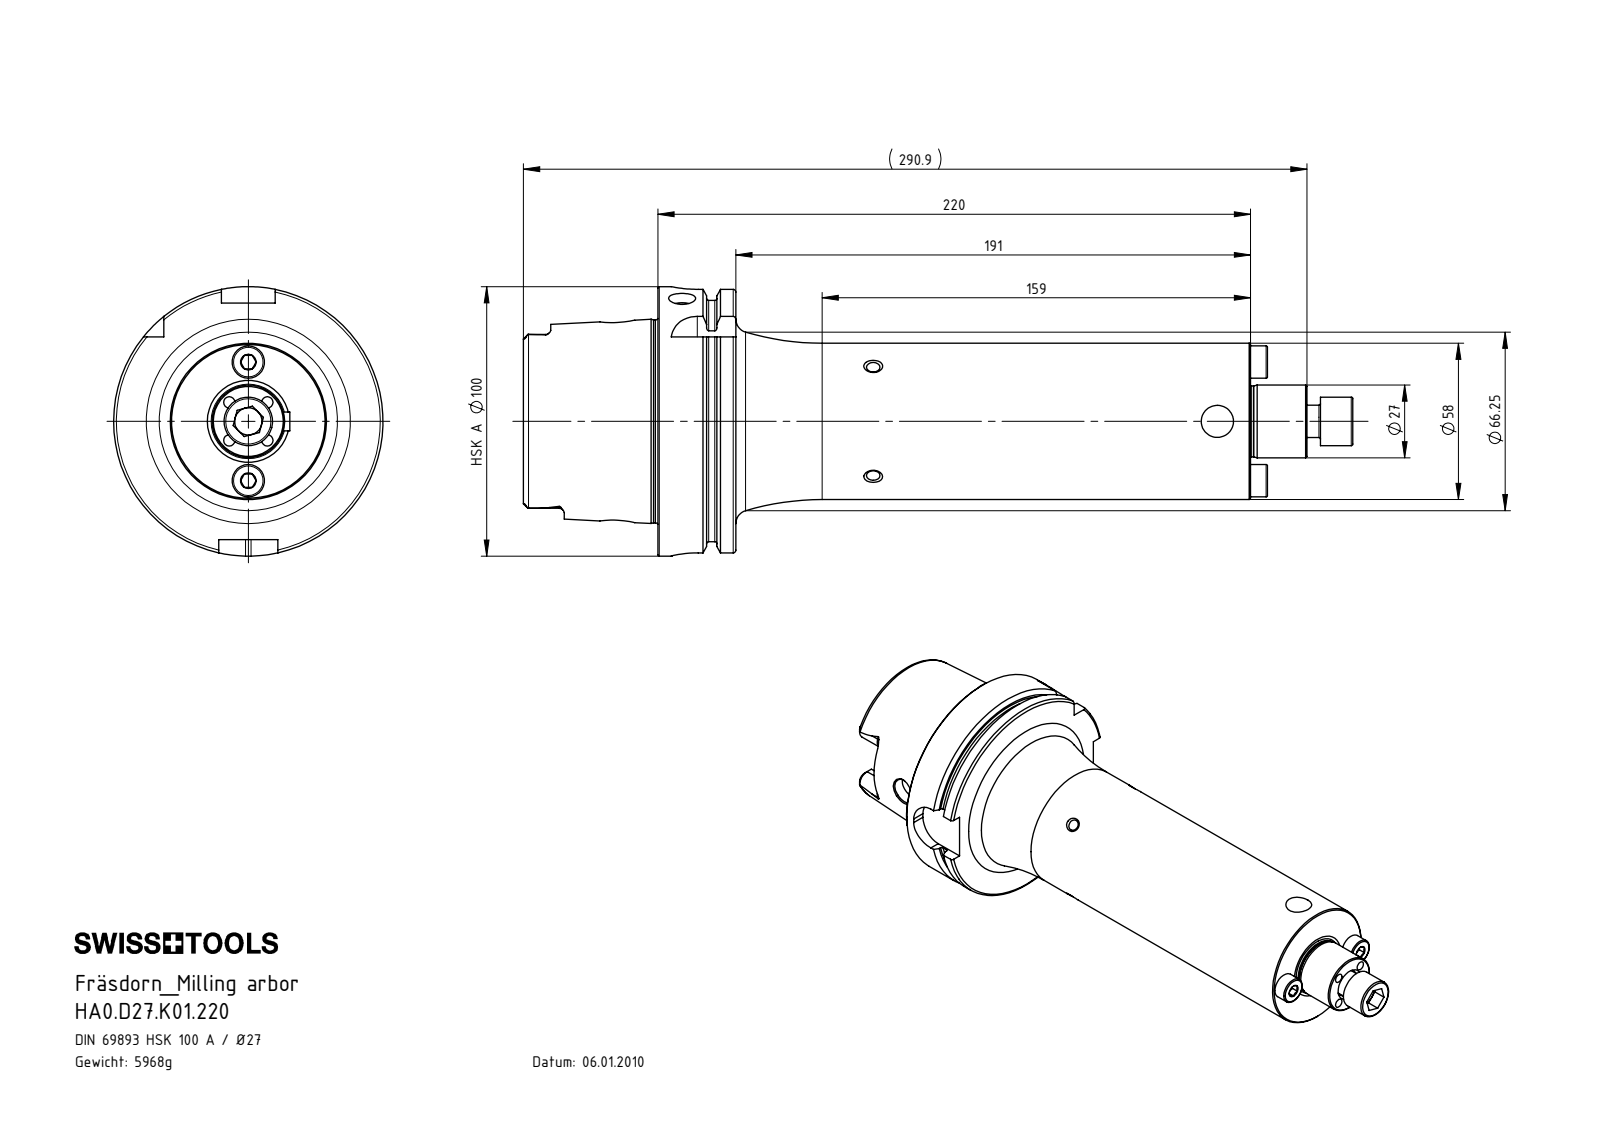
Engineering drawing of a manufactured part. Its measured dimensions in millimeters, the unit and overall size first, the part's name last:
Units: millimetres
Overall size (bounding box): 307.9 × 100 × 100
Round holes (diameter × count): ⌀4.2 ×6, ⌀5 ×6, ⌀10 ×5, ⌀12 ×2, ⌀10.2 ×1, ⌀13 ×1, ⌀22.5 ×1, ⌀26 ×1, ⌀53 ×1, ⌀63 ×1
Round bosses / shafts (diameter × count): ⌀12 ×2, ⌀6 ×2, ⌀4.6 ×2, ⌀100 ×1, ⌀91.95 ×1, ⌀75.26 ×1, ⌀58 ×1, ⌀27 ×1
Partial cylindrical surfaces — rounded edges, fillets, slot ends (radius × count): R1.9 ×6, R4.88 ×4, R10 ×4, R3.5 ×2, R4 ×2
Main face-to-face distances: 28.95, 220, 191.05, 12.45, 16.5, 207.55, 49.9, 62.35, 78.85, 269.9
Hole centre spacings: 10, 14.14, 16.52, 29.92, 130.05, 20, 22, 44
Volume: 760 258 mm³ · Surface area: 102 154 mm²
Bodies: 5 solids, 372 faces (89 planar, 118 cylindrical, 165 other)
Part name (STEP PRODUCT): HA0-D27.K01.220_C_Fertigbearbeitung; D27-ER3.001.016_A; D27-ER1.002.030_A; HA0.D27.K01.220 (+1 more)
STEP written by: SolidWorks 2017 (AUTOMOTIVE_DESIGN)
